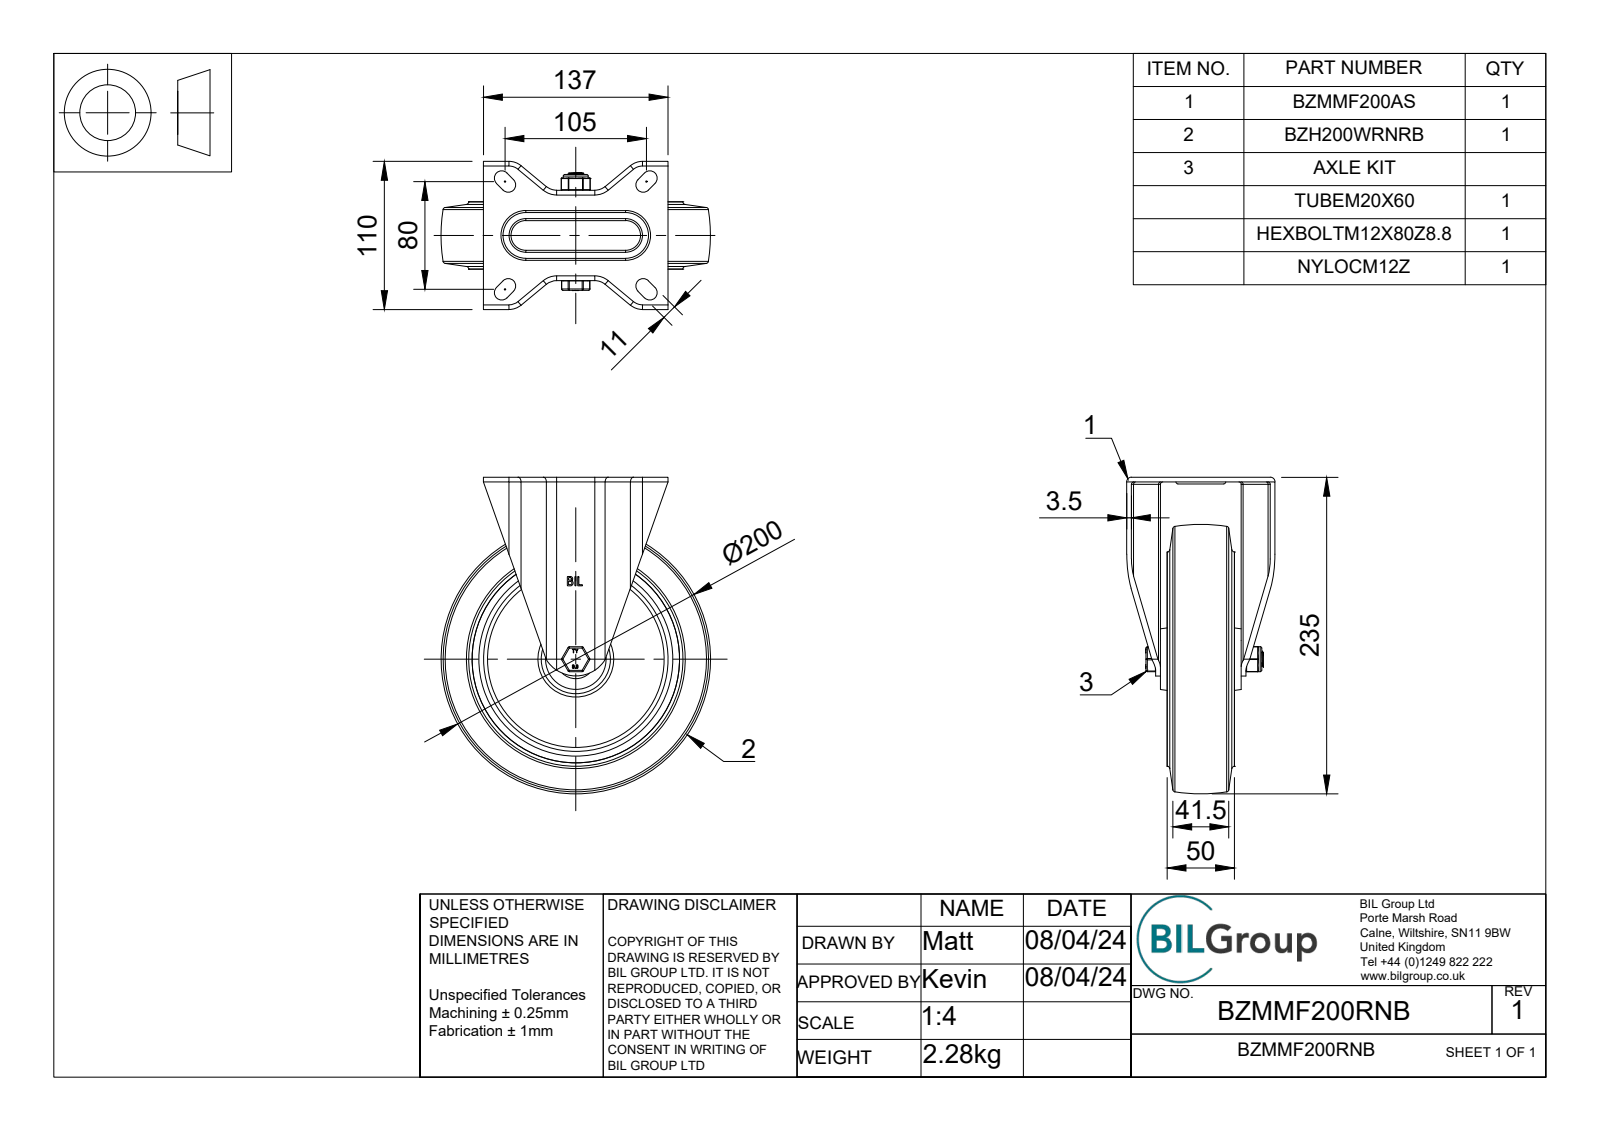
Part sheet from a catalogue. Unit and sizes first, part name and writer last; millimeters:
Units: millimetres
Overall size (bounding box): 235 × 200 × 110
Round holes (diameter × count): ⌀4.7 ×10, ⌀12 ×1, ⌀12.2 ×1, ⌀12.5 ×1, ⌀14 ×1, ⌀20 ×1, ⌀29 ×1, ⌀154 ×1
Round bosses / shafts (diameter × count): ⌀4.5 ×10, ⌀159 ×1, ⌀19.9 ×1, ⌀18.5 ×1, ⌀18 ×1, ⌀10 ×1
Partial cylindrical surfaces — rounded edges, fillets, slot ends (radius × count): R0.5 ×18, R1 ×12, R1.5 ×8, R1.75 ×8, R3.5 ×8, R5.5 ×8, R6 ×4, R7 ×4
Main face-to-face distances: 3.5, 9, 25.5, 34.5, 24.6, 29, 5, 38, 63.5, 55
Hole centre spacings: 12.25, 14.4, 19.82, 23.3, 7.57, 24.5, 7.58
Volume: 1 085 000 mm³ · Surface area: 277 273 mm²
Bodies: 18 solids, 436 faces (173 planar, 155 cylindrical, 108 other)
Part name (STEP PRODUCT): BZMMF200RNB v4; BZMMF200AS v1; BZMMF200AS; ZINC PLATED, PRESSED STEEL BRACKET (+7 more)
STEP written by: Autodesk Translation Framework v12.20.1.177 (AUTOMOTIVE_DESIGN)
